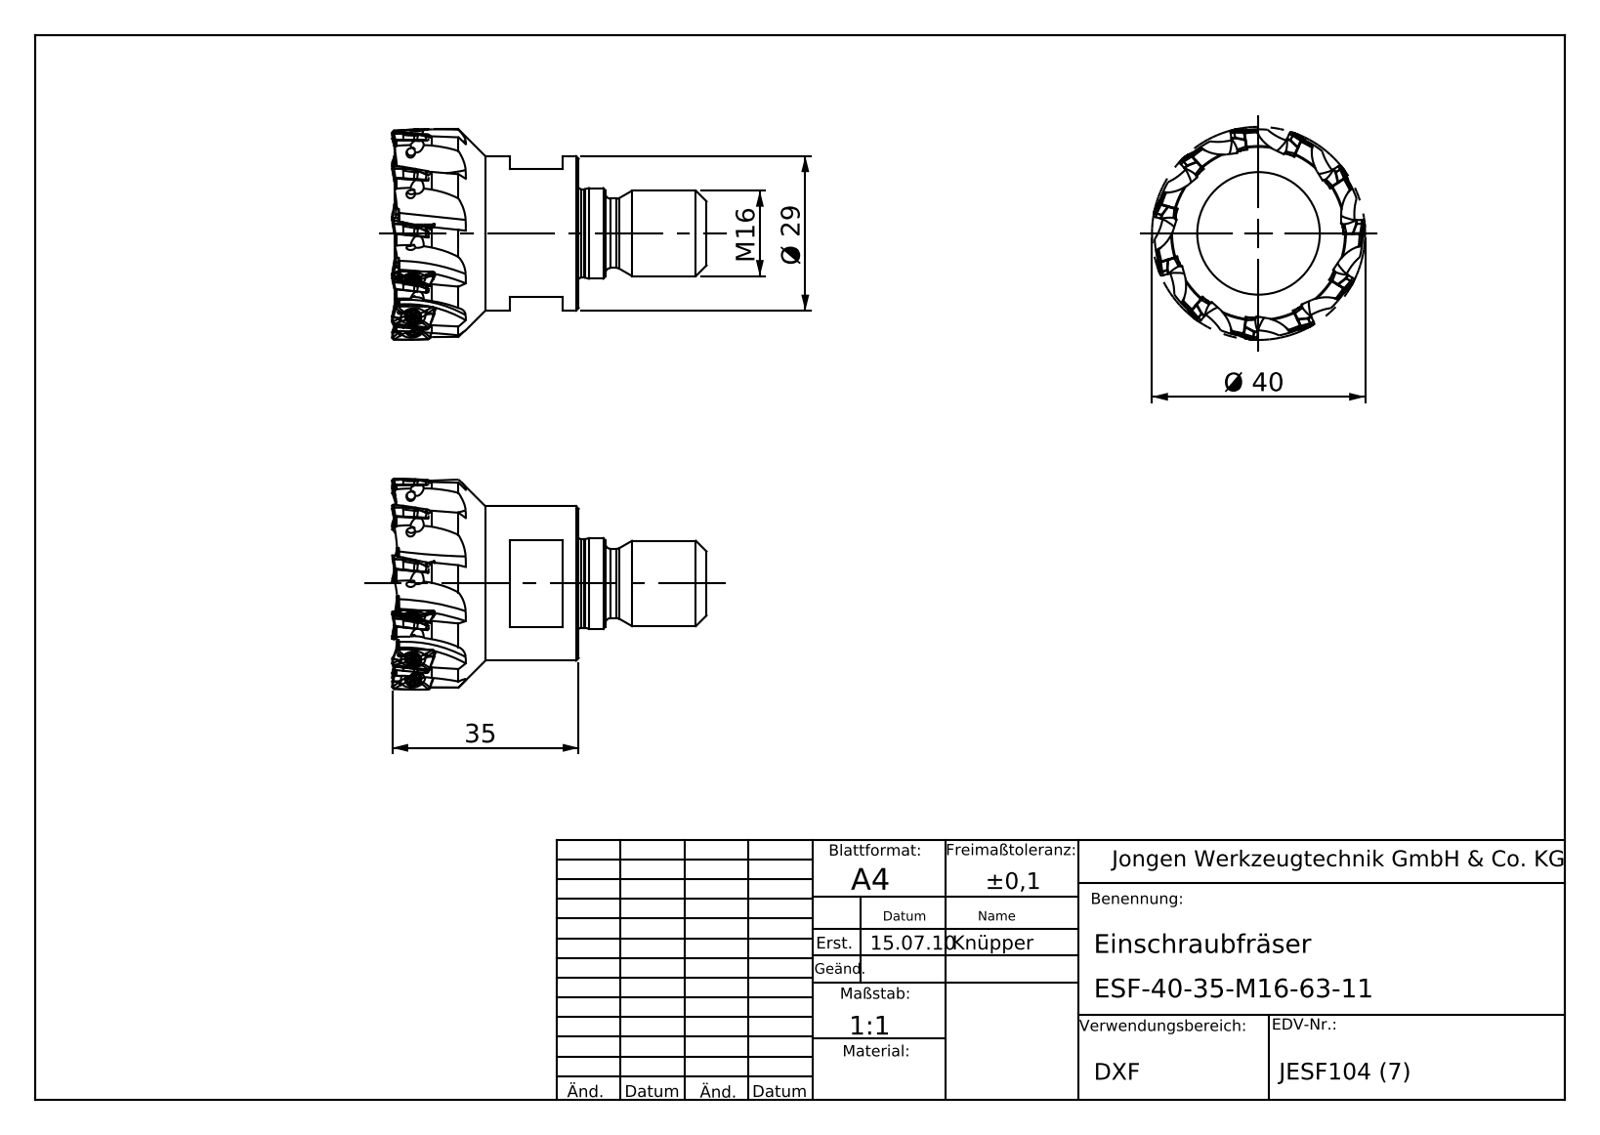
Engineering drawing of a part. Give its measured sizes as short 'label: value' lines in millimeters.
name: ESF-40-35-M16-63-11
written by: SolidWorks 2011 (AUTOMOTIVE_DESIGN)
unit: mm
bodies: 1 solid, 279 faces (88 planar, 78 cylindrical, 113 other)
size: 59 × 40 × 40
volume: 30 888 mm³; area: 10 774 mm²
holes: 11× ⌀2.5, 1× ⌀4
bosses: 1× ⌀29, 1× ⌀17, 1× ⌀16.6, 1× ⌀16, 1× ⌀13
rounds: 11× R1.25, 11× R20, 1× R19.53
face distances: 33.15, 24, 34.55, 1.4, 57.15, 58.55, 27, 37, 3, 13
